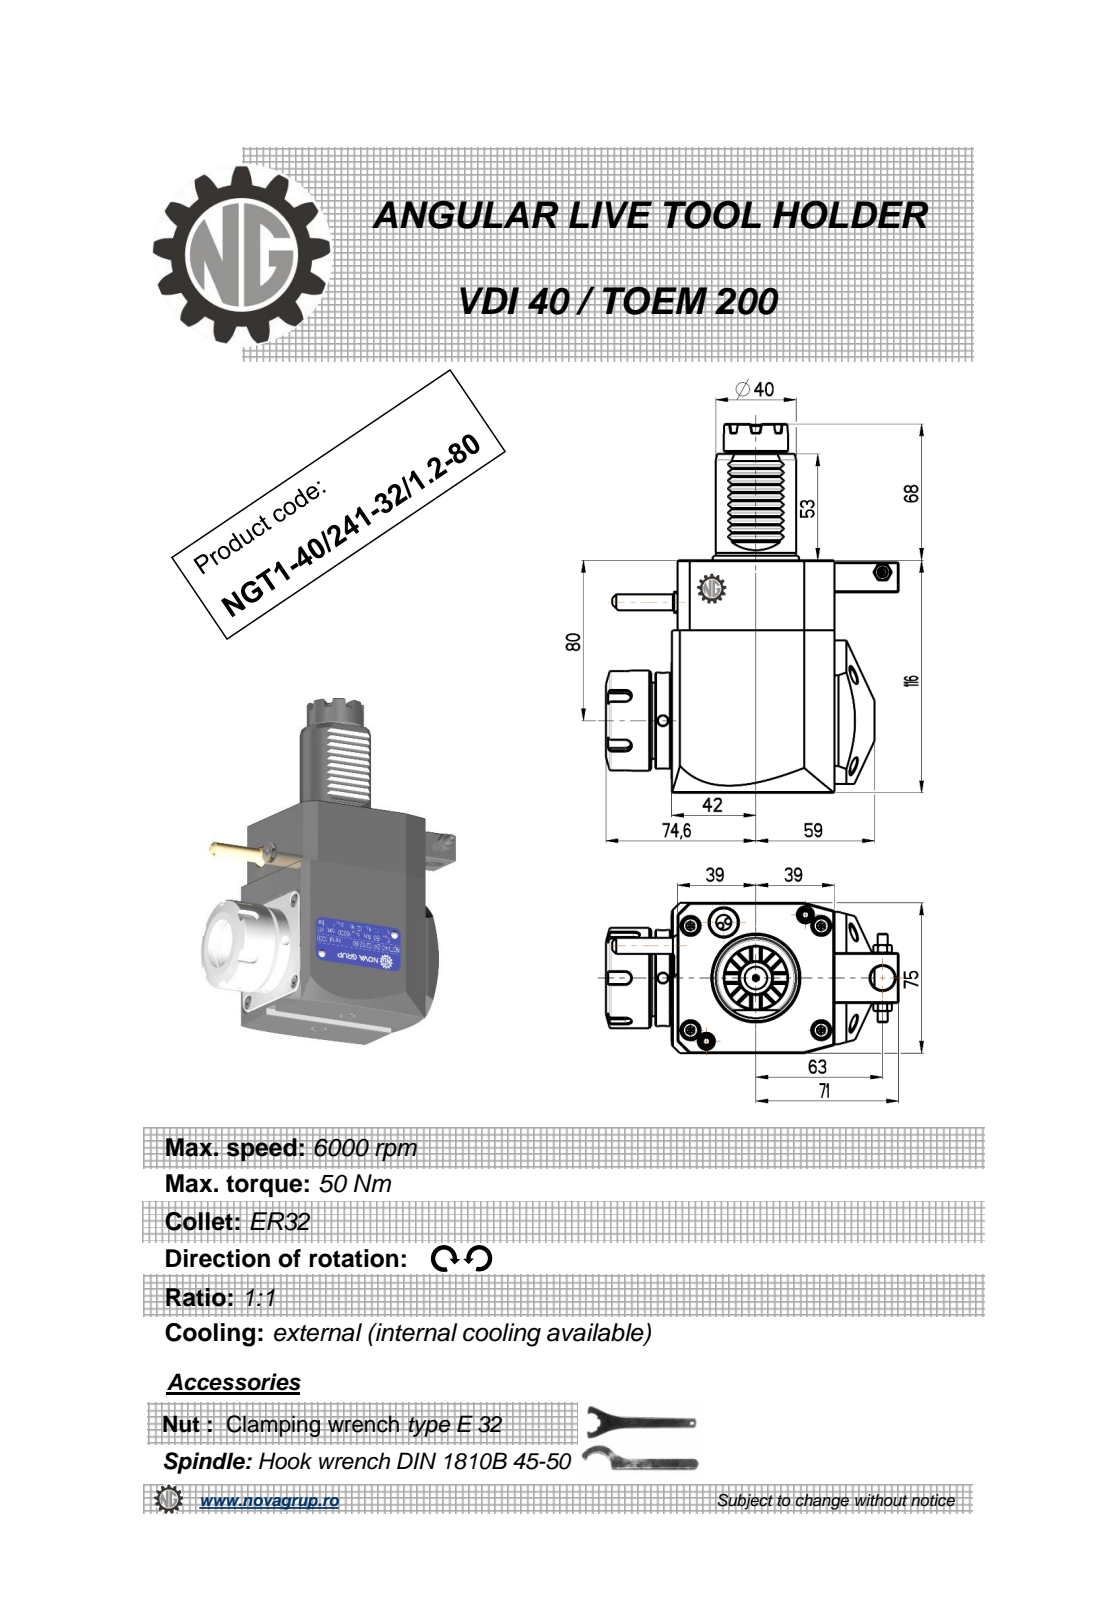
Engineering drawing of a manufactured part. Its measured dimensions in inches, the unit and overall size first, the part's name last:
Units: inches
Overall size (bounding box): 7.244 × 5.732 × 3.016
Round holes (diameter × count): ⌀0.197 ×3, ⌀0.118 ×1, ⌀0.165 ×1, ⌀0.374 ×1, ⌀0.472 ×1, ⌀1.063 ×1
Round bosses / shafts (diameter × count): ⌀1.969 ×1, ⌀1.89 ×1, ⌀1.614 ×1, ⌀1.575 ×1, ⌀1.26 ×1, ⌀0.669 ×1, ⌀0.441 ×1, ⌀0.353 ×1
Partial cylindrical surfaces — rounded edges, fillets, slot ends (radius × count): R0.01 ×12, R0.012 ×10, R0.009 ×6, R0.118 ×5, R0.02 ×1, R0.339 ×1, R1.575 ×1
Main face-to-face distances: 2.953, 4.567, 3.189, 3.071, 0.118, 0.11, 3.181, 0.984, 0.177, 0.039
Hole centre spacings: 0.824, 2.407, 2.854, 4.301, 5.195
Volume: 53.55 in³ · Surface area: 110.7 in²
Bodies: 1 solid, 485 faces (221 planar, 97 cylindrical, 167 other)
Part name (STEP PRODUCT): NGT1_40_241_32_1_2_80
STEP written by: PRO/ENGINEER BY PARAMETRIC TECHNOLOGY CORPORATION, 2010280 (CONFIG_CONTROL_DESIGN)
